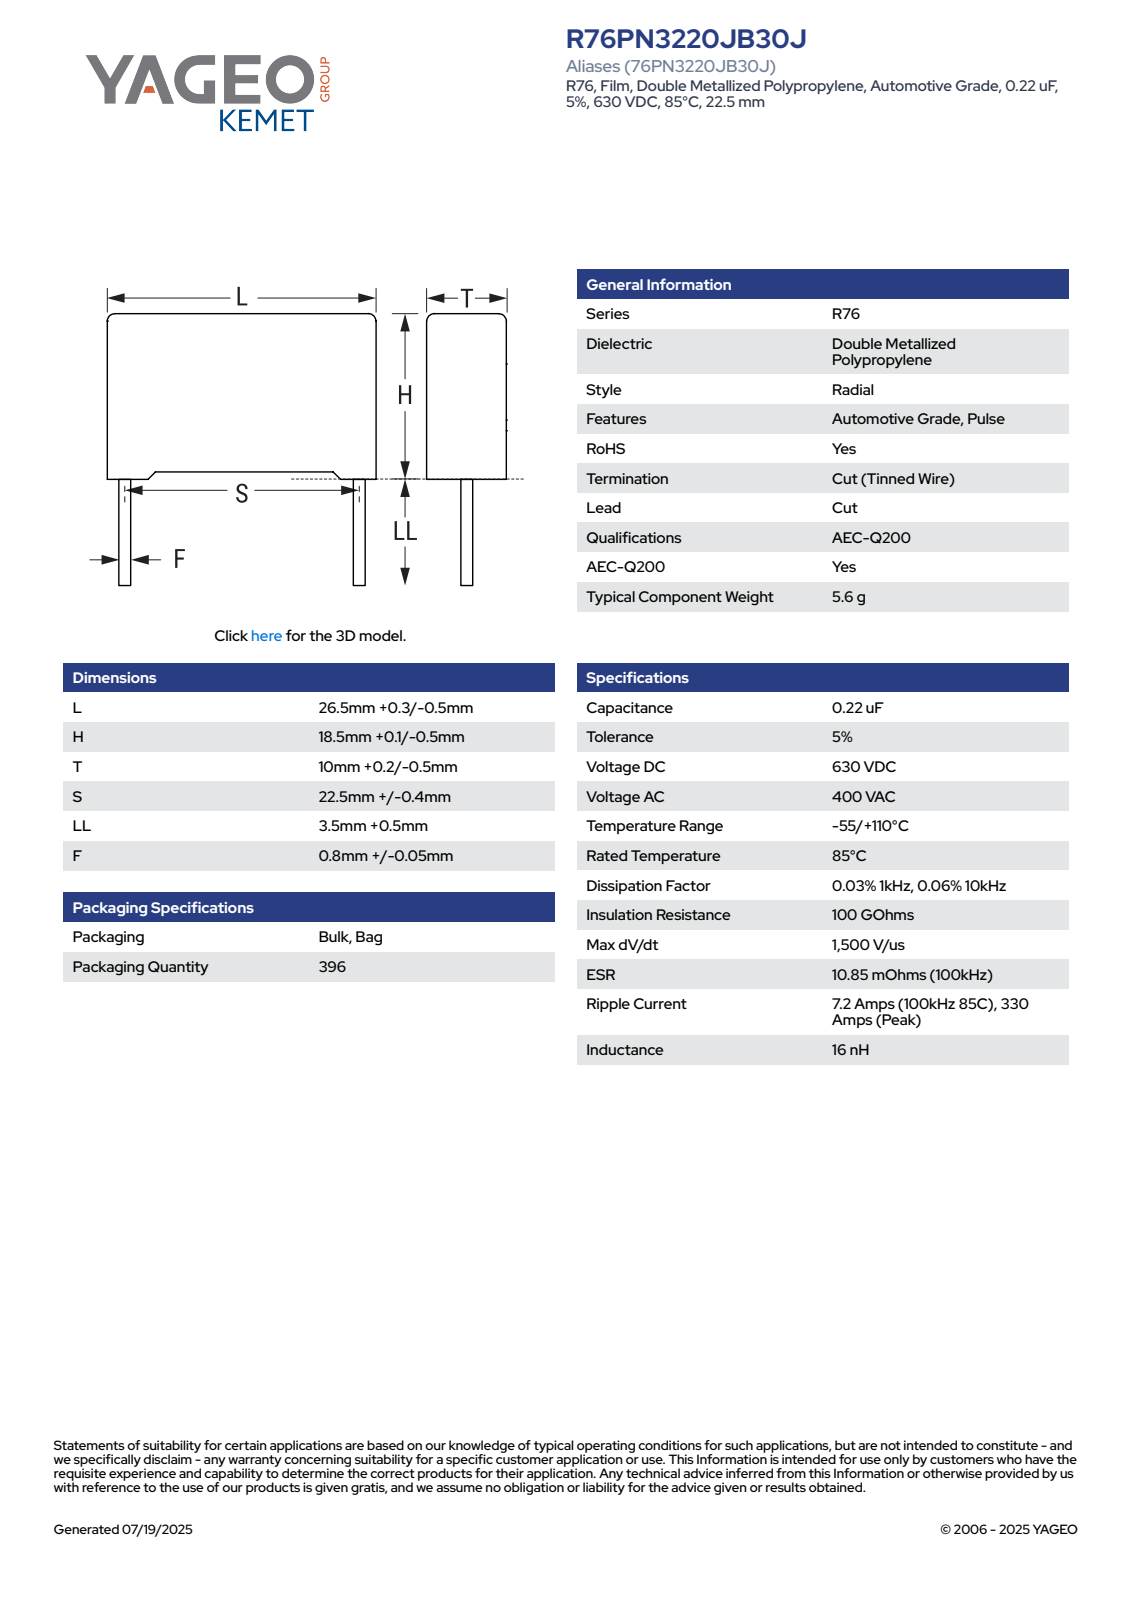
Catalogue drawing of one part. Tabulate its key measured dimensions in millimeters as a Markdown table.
| quantity | value |
| --- | --- |
| part name | CFR_RB2_26.5X18.5X10_L26.8H18.6T10.2S22.5LL4F0.85 |
| STEP written by | SolidWorks 2021 (AUTOMOTIVE_DESIGN) |
| units | millimeters |
| bodies | 4 solids, 85 faces (77 planar, 8 cylindrical, 0 other) |
| overall size | 26.8 × 22.6 × 10.21 |
| volume | 4 907 mm³ |
| surface area | 1 989 mm² |
| round bosses / shafts (diameter × count) | 0.85 × 2 |
| partial cylindrical surfaces (radius × count) | 0.5 × 4 |
| main face-to-face distances | 10.2, 17.85, 26.8, 17.96, 0.75, 0.64, 18.6, 0.89, 9.31, 25.91 |
